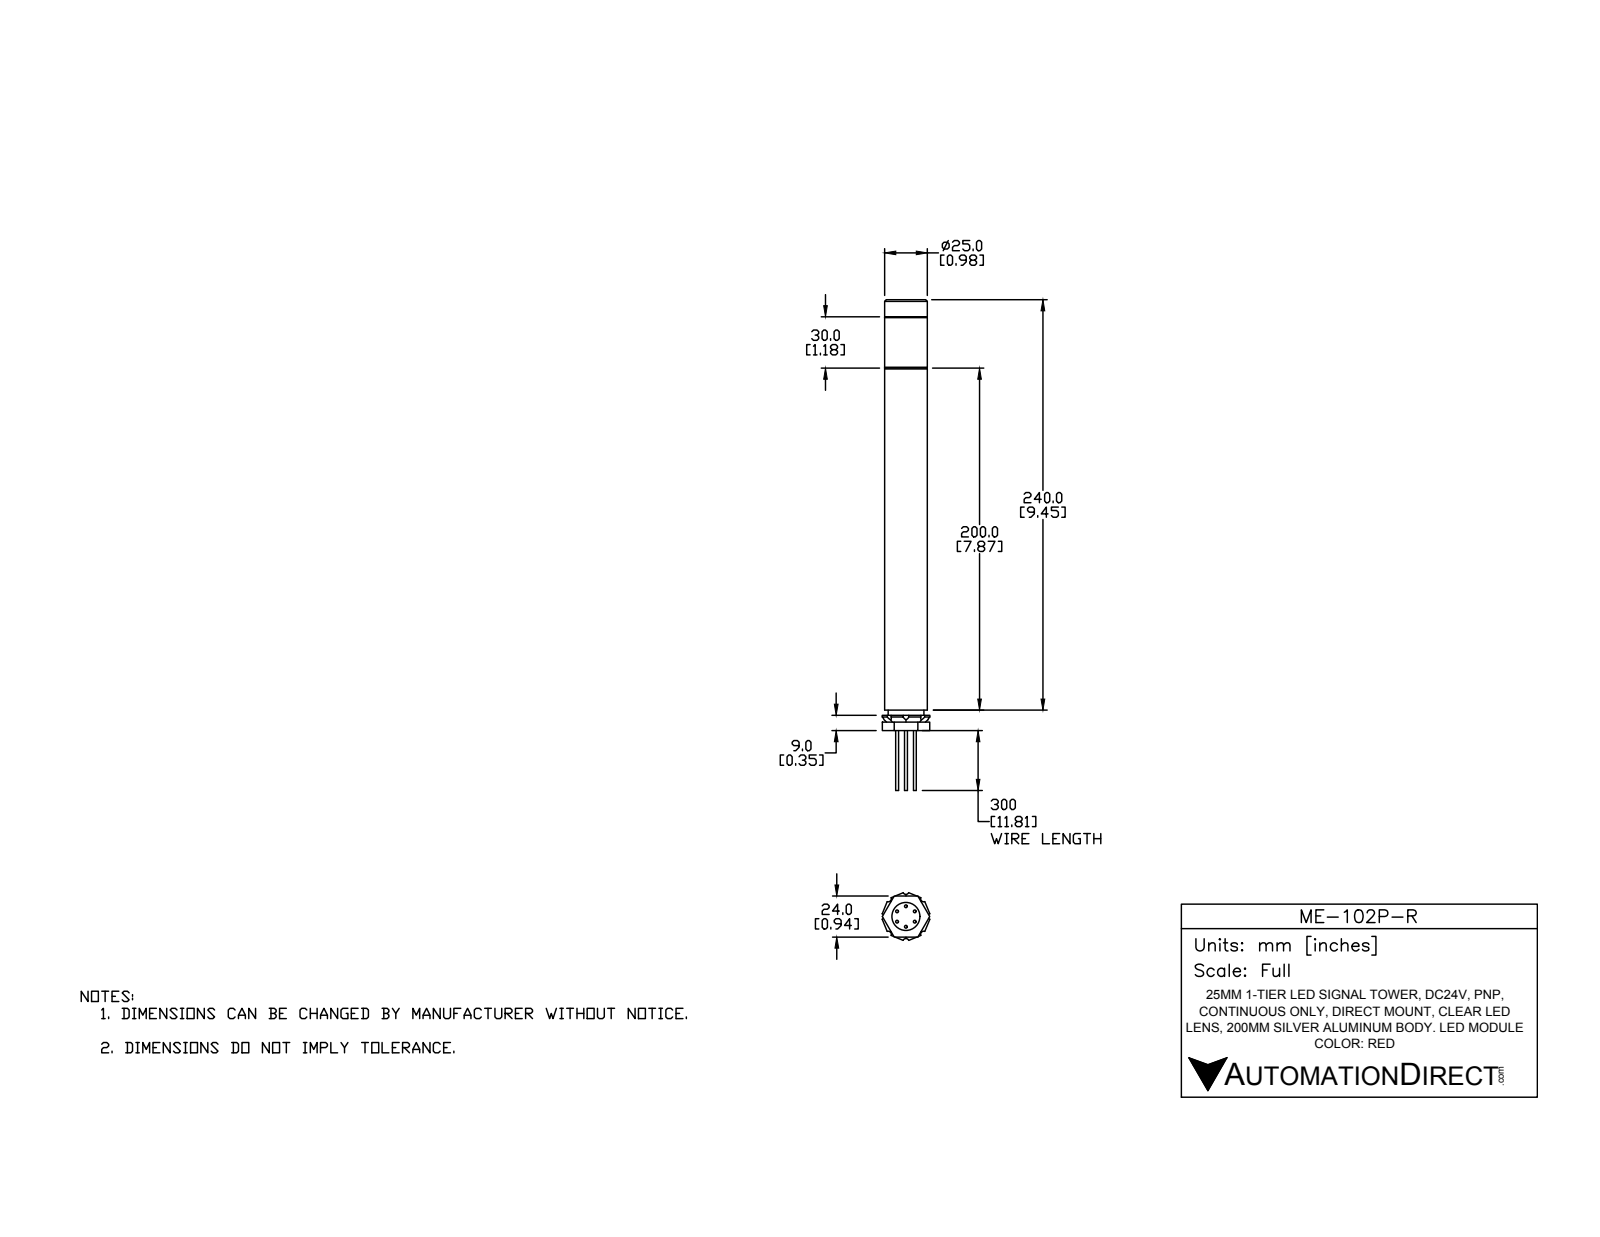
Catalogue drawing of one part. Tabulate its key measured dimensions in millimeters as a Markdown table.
| quantity | value |
| --- | --- |
| part name | ME-102P-R |
| STEP written by | SolidWorks 2016 (AUTOMOTIVE_DESIGN) |
| units | millimeters |
| bodies | 12 solids, 132 faces (71 planar, 47 cylindrical, 14 other) |
| overall size | 287 × 27.89 × 27.89 |
| volume | 112 181 mm³ |
| surface area | 31 231 mm² |
| round holes (diameter × count) | 3.2 × 1, 7.7 × 1, 16.4 × 1, 18 × 1, 20.7 × 1, 21 × 1 |
| round bosses / shafts (diameter × count) | 1.7 × 6, 25 × 1, 20.9 × 1, 16 × 1, 5 × 1 |
| partial cylindrical surfaces (radius × count) | 1.75 × 8 |
| main face-to-face distances | 30, 40, 207, 167, 197, 10, 45, 212, 242, 252 |
